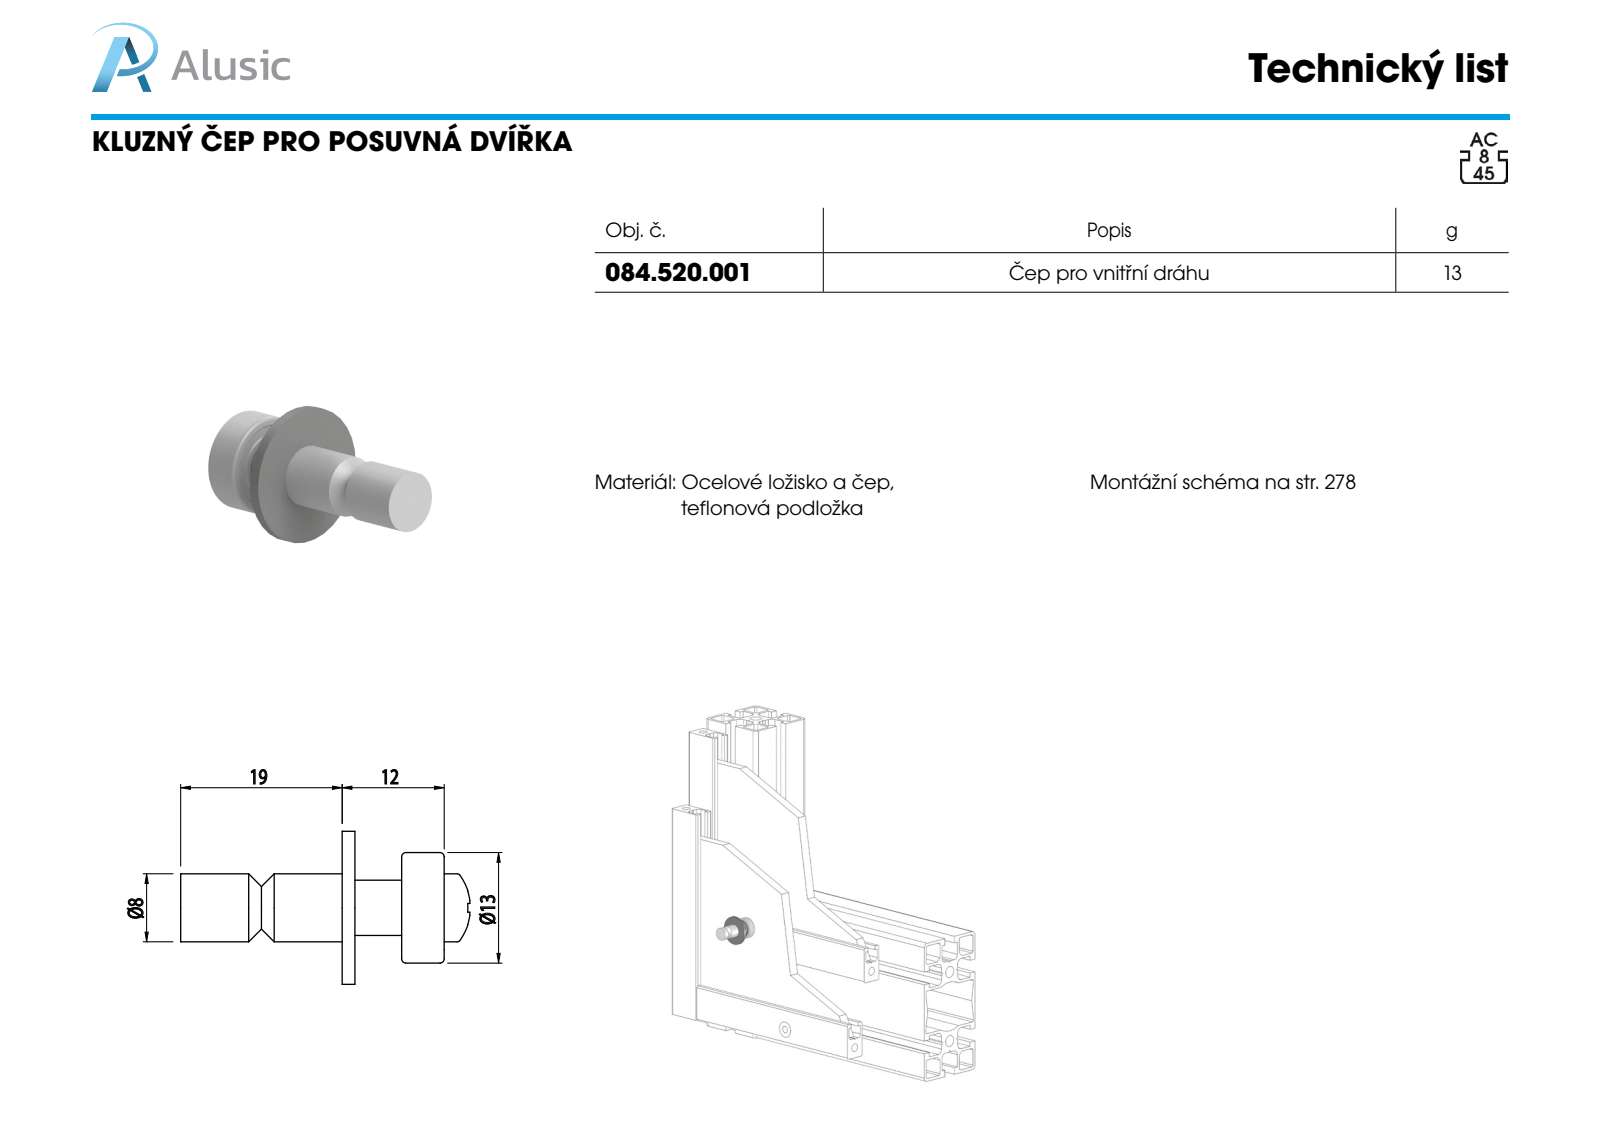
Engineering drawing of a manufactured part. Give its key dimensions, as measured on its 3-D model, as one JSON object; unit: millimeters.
{"part_name": "CUSCINETTI A SFERE_686-ZZ; RT; 700026; 084.520.001", "step_written_by": "SolidWorks 2011 (CONFIG_CONTROL_DESIGN)", "units": "millimeters", "bodies": {"solids": 3, "faces": 52, "planar": 12, "cylindrical": 18, "other": 22}, "overall_size": [31, 18, 18], "volume_mm3": 1997, "surface_area_mm2": 1993, "round_holes": [[3.3, 1], [6, 1], [7, 1]], "round_bosses_or_shafts": [[18, 1], [13, 1], [8, 1], [6.5, 1]], "face_to_face_distances": [1.5, 20.5, 19, 10.5, 12, 31, 5, 5.5, 7, 26]}
